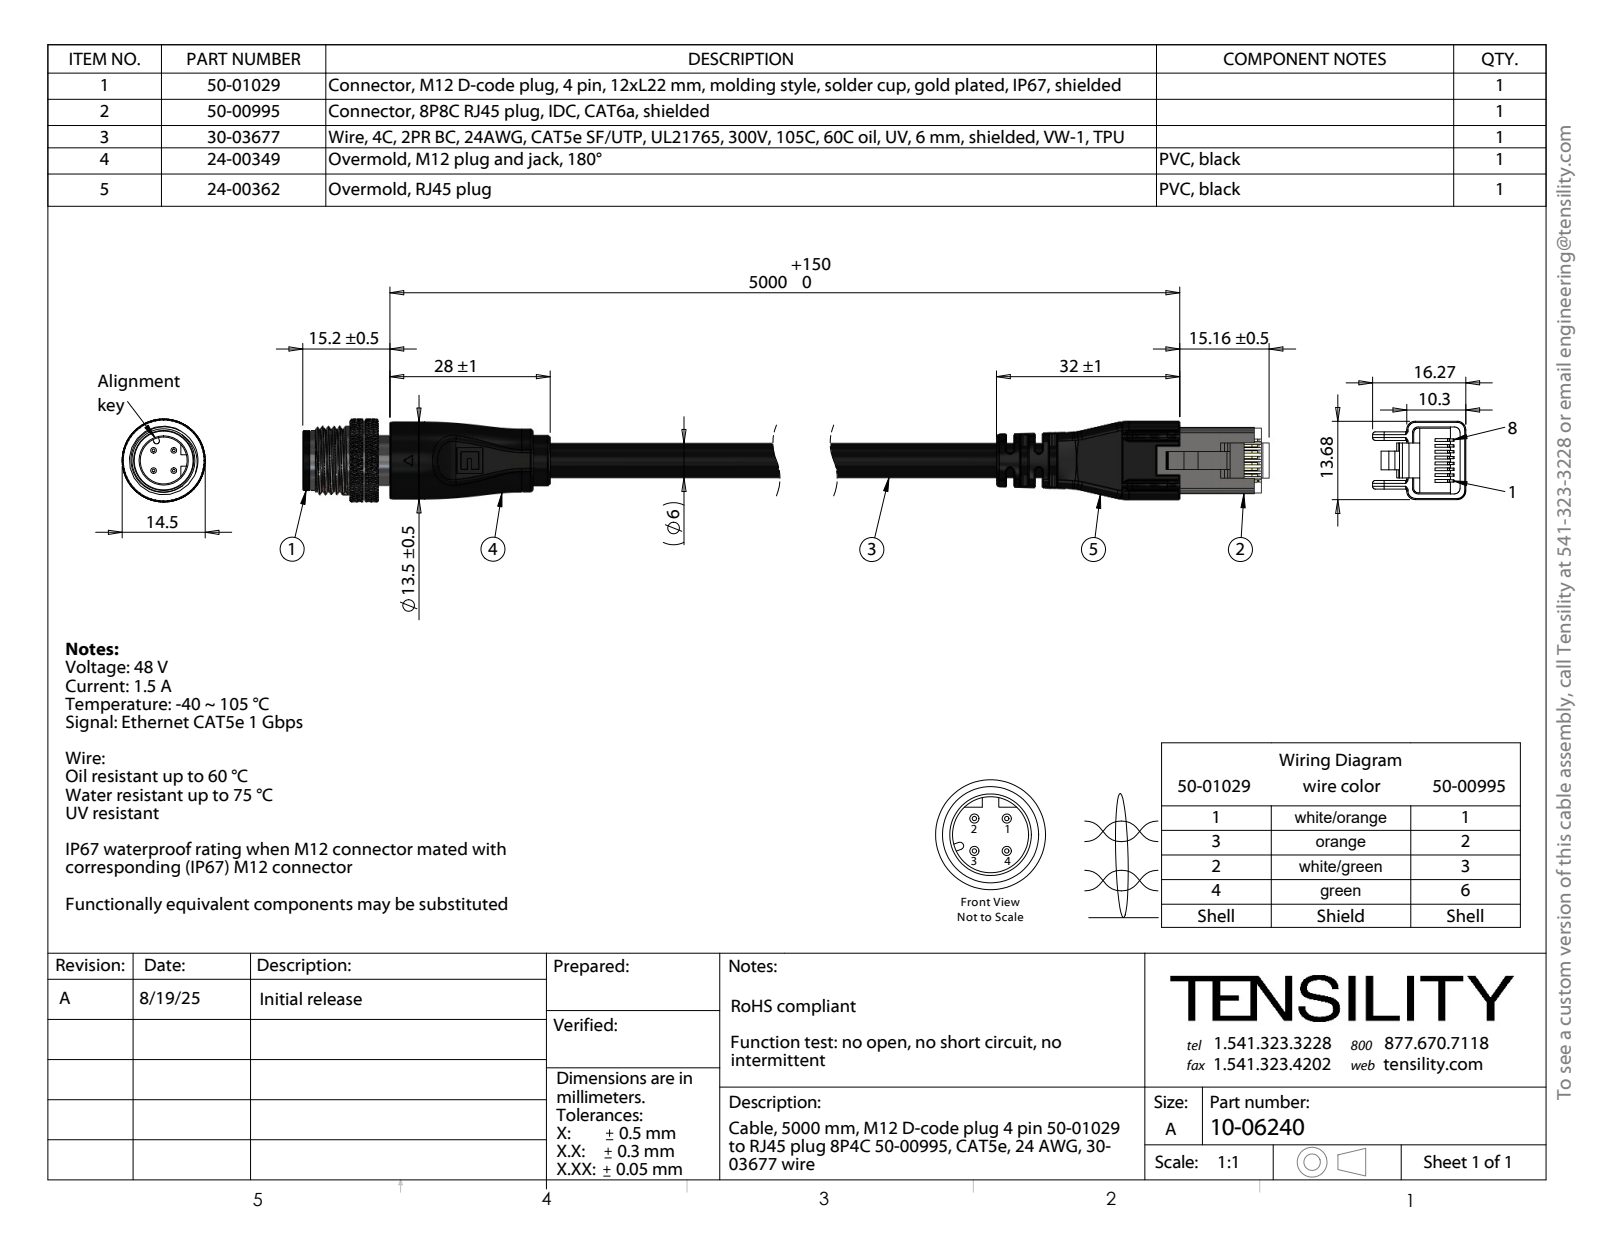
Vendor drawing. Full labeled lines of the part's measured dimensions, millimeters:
Part name (STEP PRODUCT): 24-00362; 24-00349_Mexico; 50-00995; 50-01029-03_默认 (+6 more)
STEP written by: SolidWorks 2025 (CONFIG_CONTROL_DESIGN)
Units: millimetres
Bodies: 54 solids, 3209 faces (470 planar, 811 cylindrical, 1928 other)
Overall size (bounding box): 230.31 × 18.37 × 14.5
Volume: 13 919 mm³ · Surface area: 29 131 mm²
Round holes (diameter × count): ⌀0.2 ×28, ⌀1 ×4, ⌀1.05 ×4, ⌀3.16 ×1, ⌀3.21 ×1, ⌀3.56 ×1, ⌀8 ×1, ⌀8.2 ×1, ⌀8.8 ×1, ⌀9.5 ×1
Round bosses / shafts (diameter × count): ⌀1.4 ×4, ⌀14.5 ×1, ⌀13.9 ×1, ⌀13.5 ×1, ⌀12 ×1, ⌀11 ×1, ⌀10.5 ×1, ⌀9.3 ×1
Partial cylindrical surfaces — rounded edges, fillets, slot ends (radius × count): R0.2 ×11, R0.5 ×10, R1.5 ×10, R0.62 ×8, R1 ×5, R10 ×4, R0.8 ×2, R1.15 ×2
Main face-to-face distances: 1.25, 2.5, 1, 3.75, 5, 9.3, 7, 199.5, 12.68, 11.68
Hole centre spacings: 1.06, 1.91, 2.09, 0.35, 1.08, 1.71, 1.8, 2.26
